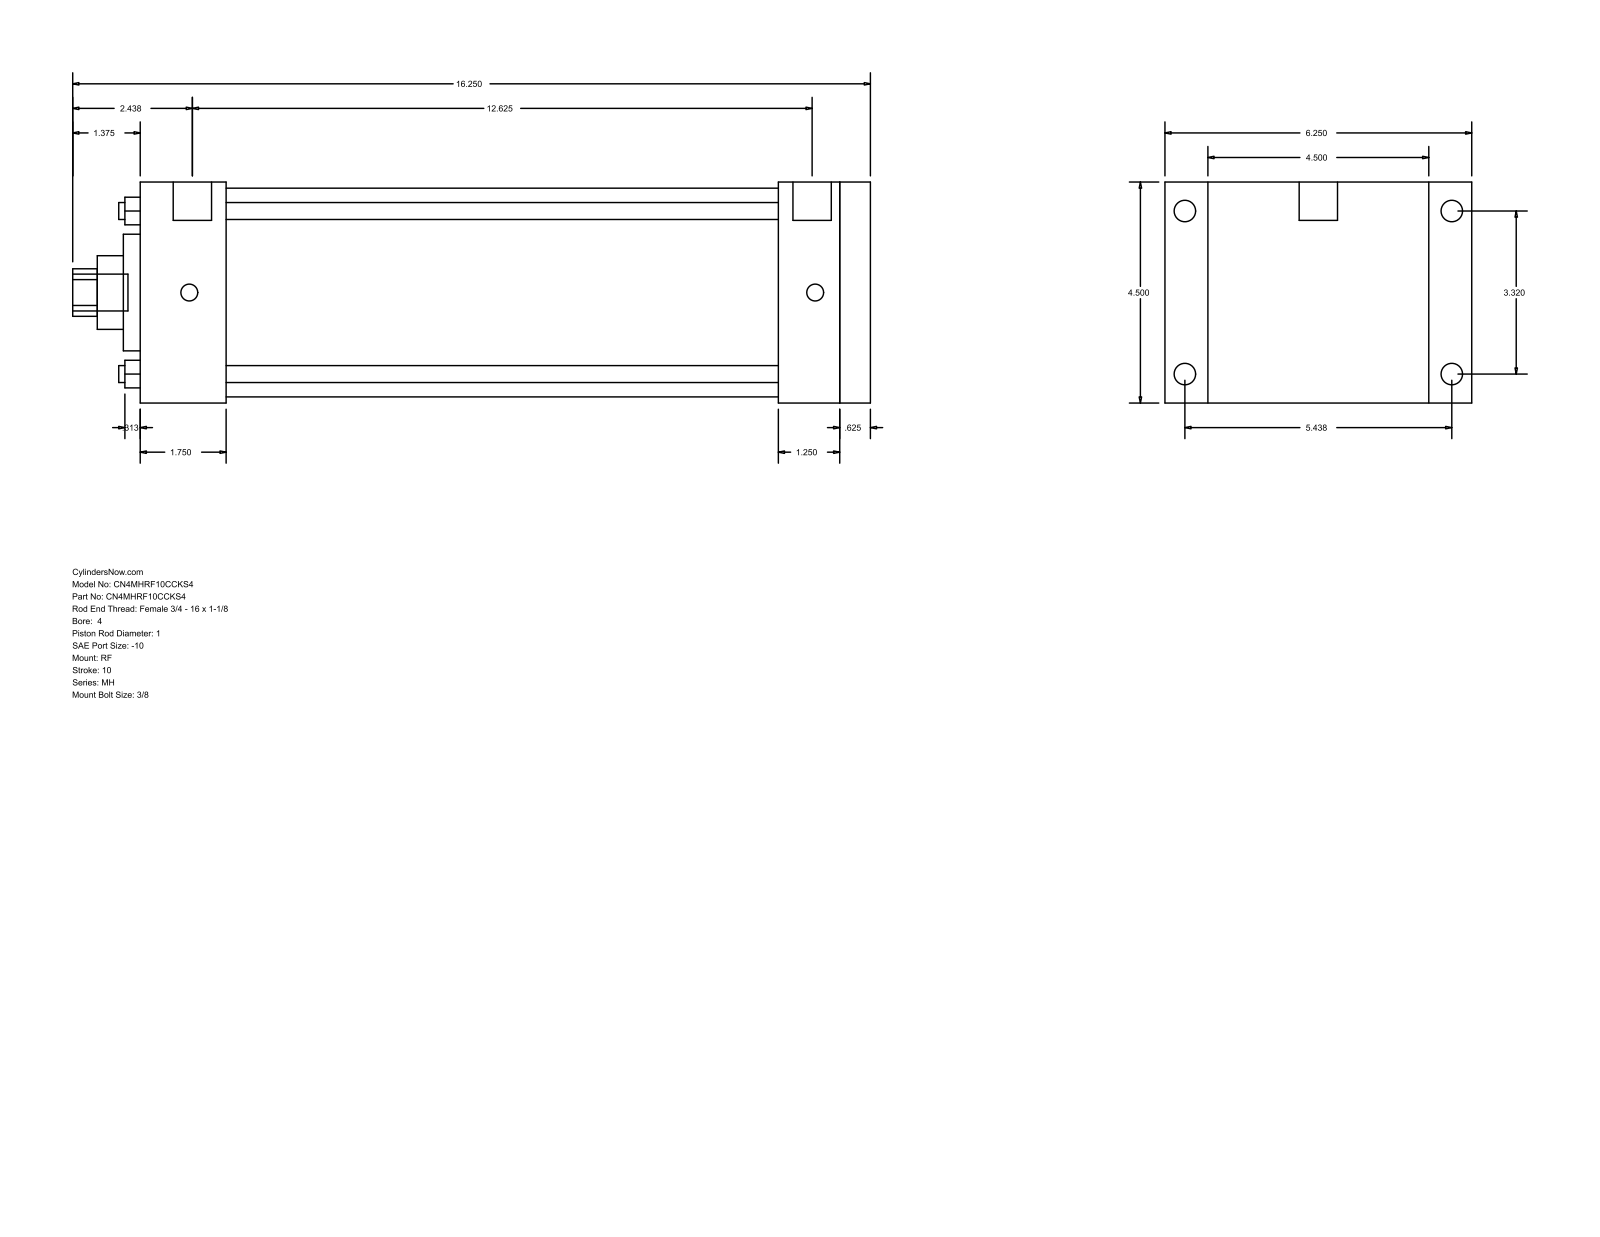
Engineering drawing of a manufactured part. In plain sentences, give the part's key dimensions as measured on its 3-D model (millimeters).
The part is named "MH_RF__0400_1". Its 3-D file was written by "GSSL Pune (CONFIG_CONTROL_DESIGN)". It is 0 solids with 94 faces: 65 planar, 29 cylindrical and 0 other. Overall it measures 412.75 by 158.75 by 114.3 millimeters. Round holes: 4 of diameter 8.76, 1 of diameter 25.4, 1 of diameter 38.1, 1 of diameter 60.33, 1 of diameter 107.95. Round bosses or shafts: 4 of diameter 11.13, 4 of diameter 8.73, 2 of diameter 19.84, 1 of diameter 19.05. Partial cylindrical surfaces (rounded edges, fillets, slot ends): 1 of radius 12.29. The main face-to-face distances are 114.3, 377.83, 15.87, 361.96, 47.63, 44.46, 317.5, 333.37, 330.2, 285.74. The hole center spacings are 59.62, 84.32, 119.25.
